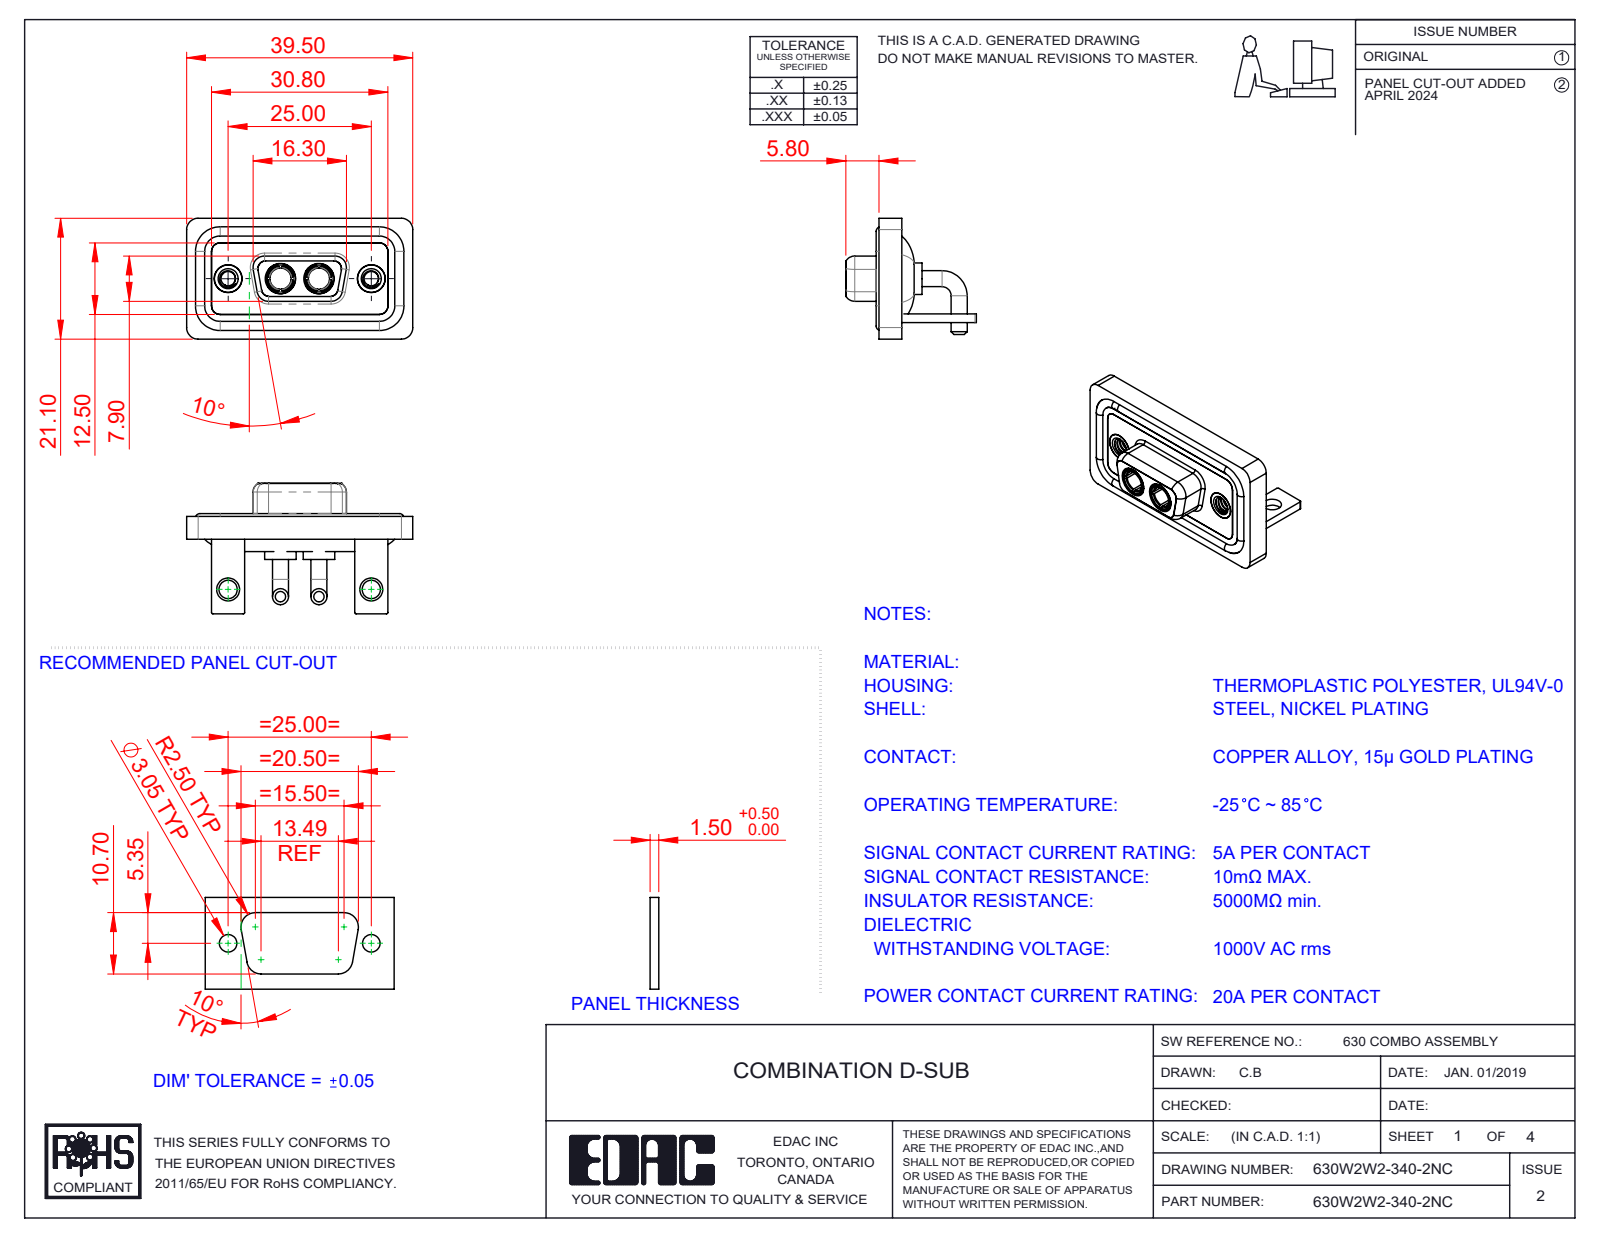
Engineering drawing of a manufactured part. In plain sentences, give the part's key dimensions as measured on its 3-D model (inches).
The part is named "630Combo Shell Rear_09 Contacts; 630Combo Housing_2W2; Power Socket_20A RA; 630Combo Stabilizer Bracket_50 Contacts (+4 more)". Its 3-D file was written by "SolidWorks 2023 (CONFIG_CONTROL_DESIGN)". It is 13 solids with 584 faces: 183 planar, 260 cylindrical and 141 other. Overall it measures 1.555 by 0.898 by 0.831 inches. Its volume is 0.316 cubic inches and its surface area 13.21 square inches. Round holes: 4 of diameter 0.191, 2 of diameter 0.098, 2 of diameter 0.126, 2 of diameter 0.146, 2 of diameter 0.157, 2 of diameter 0.159, 2 of diameter 0.197, 2 of diameter 0.209. Round bosses or shafts: 4 of diameter 0.11, 4 of diameter 0.063, 2 of diameter 0.217, 2 of diameter 0.205, 2 of diameter 0.195, 2 of diameter 0.195, 2 of diameter 0.189, 2 of diameter 0.187. Partial cylindrical surfaces (rounded edges, fillets, slot ends): 19 of radius 0.079, 18 of radius 0.059, 16 of radius 0.01, 8 of radius 0.053, 8 of radius 0.063, 5 of radius 0.02, 4 of radius 0.024, 4 of radius 0.026. The main face-to-face distances are 0.016, 0.114, 0.059, 0.071, 0.043, 0.146, 0.031, 0.098, 0.063, 0.122. The hole center spacings are 0.36, 0.624, 0.984, 0.265.
